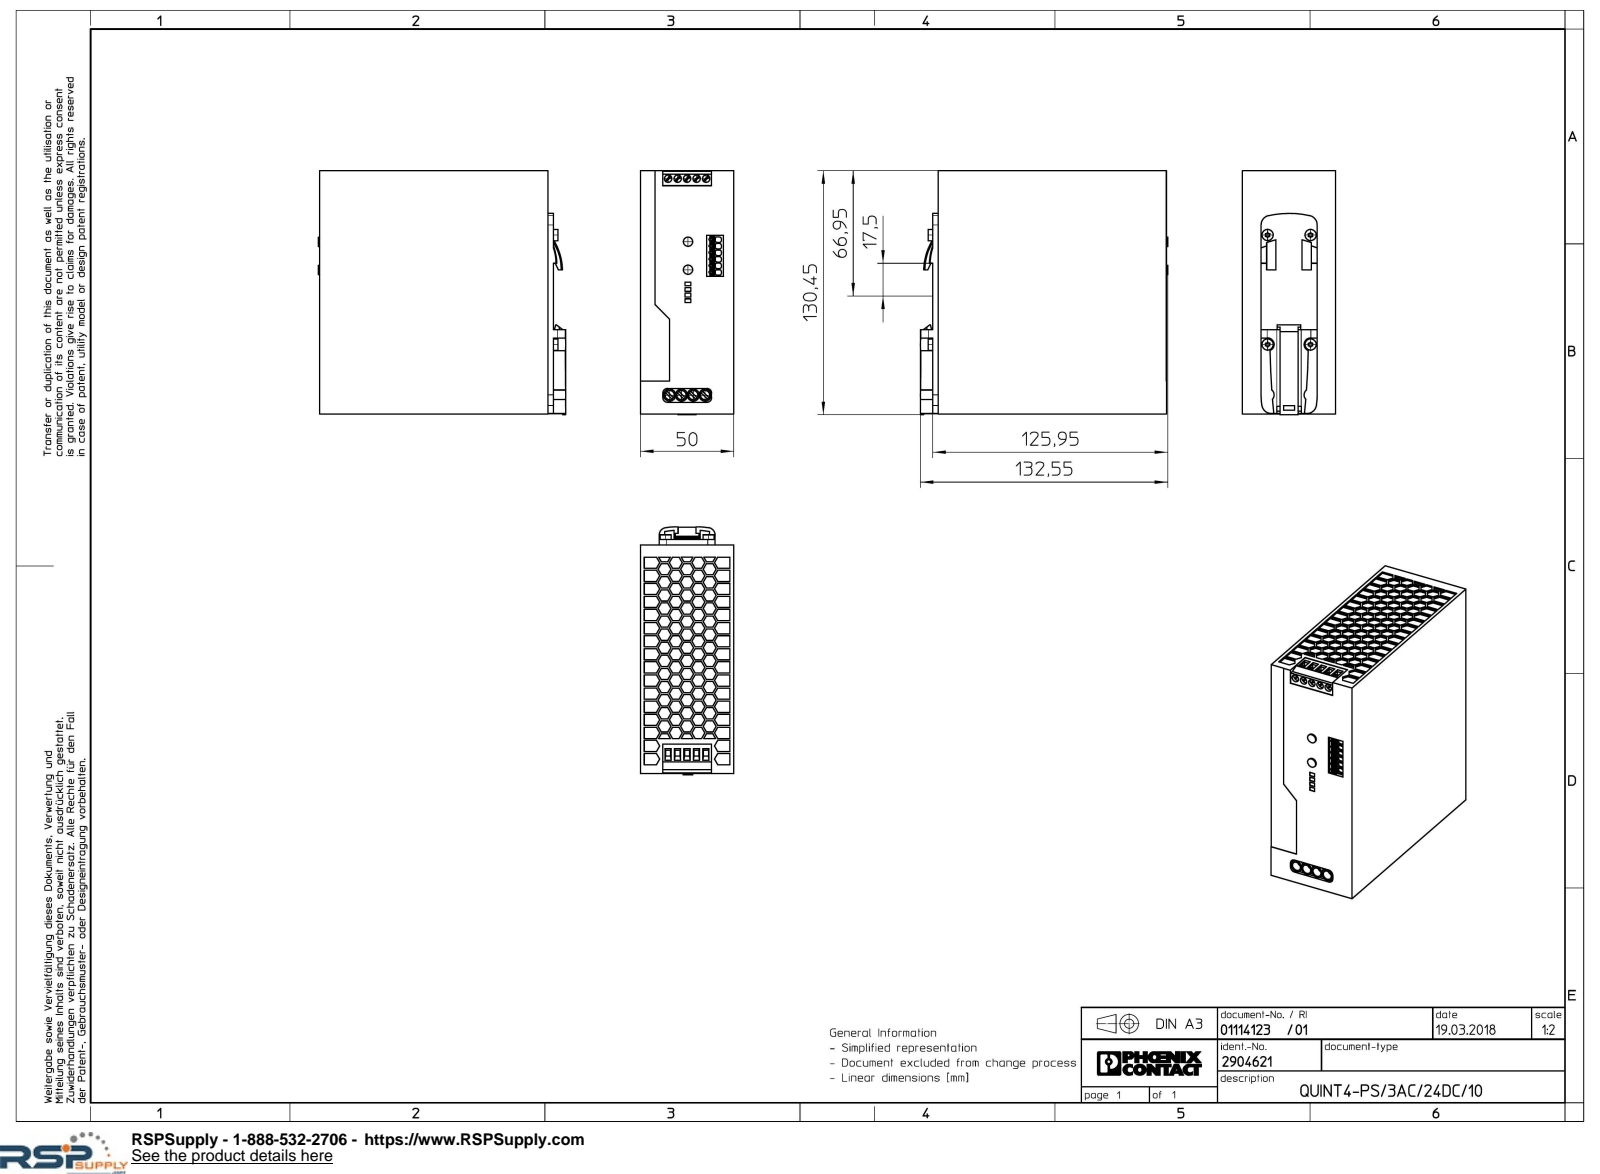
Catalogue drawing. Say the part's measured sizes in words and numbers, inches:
The part is named "QUINT4_PS_3AC_24DC_10-select". Its 3-D file was written by "Creo Elements/Direct Modeling 20.1A 29-Sep-2018 (C) Parametric Technology GmbH (AUTOMOTIVE_DESIGN)". It is 1 solid with 1971 faces: 1822 planar, 133 cylindrical and 16 other. Overall it measures 5.219 by 5.136 by 1.969 inches. Its volume is 48.93 cubic inches and its surface area 101.4 square inches. Round holes: 5 of diameter 0.157, 4 of diameter 0.197. Round bosses or shafts: 4 of diameter 0.236, 2 of diameter 0.197. Partial cylindrical surfaces (rounded edges, fillets, slot ends): 48 of radius 0.004, 12 of radius 0.038, 6 of radius 0.022, 6 of radius 0.024, 4 of radius 0.098, 4 of radius 0.128, 4 of radius 0.138, 4 of radius 0.197. The main face-to-face distances are 1.969, 0.031, 5.087, 5.055, 4.813, 5.118, 0.118, 4.931, 4.927, 4.809. The hole center spacings are 0.2, 0.25, 0.4, 0.5, 0.6, 0.75, 0.8.
